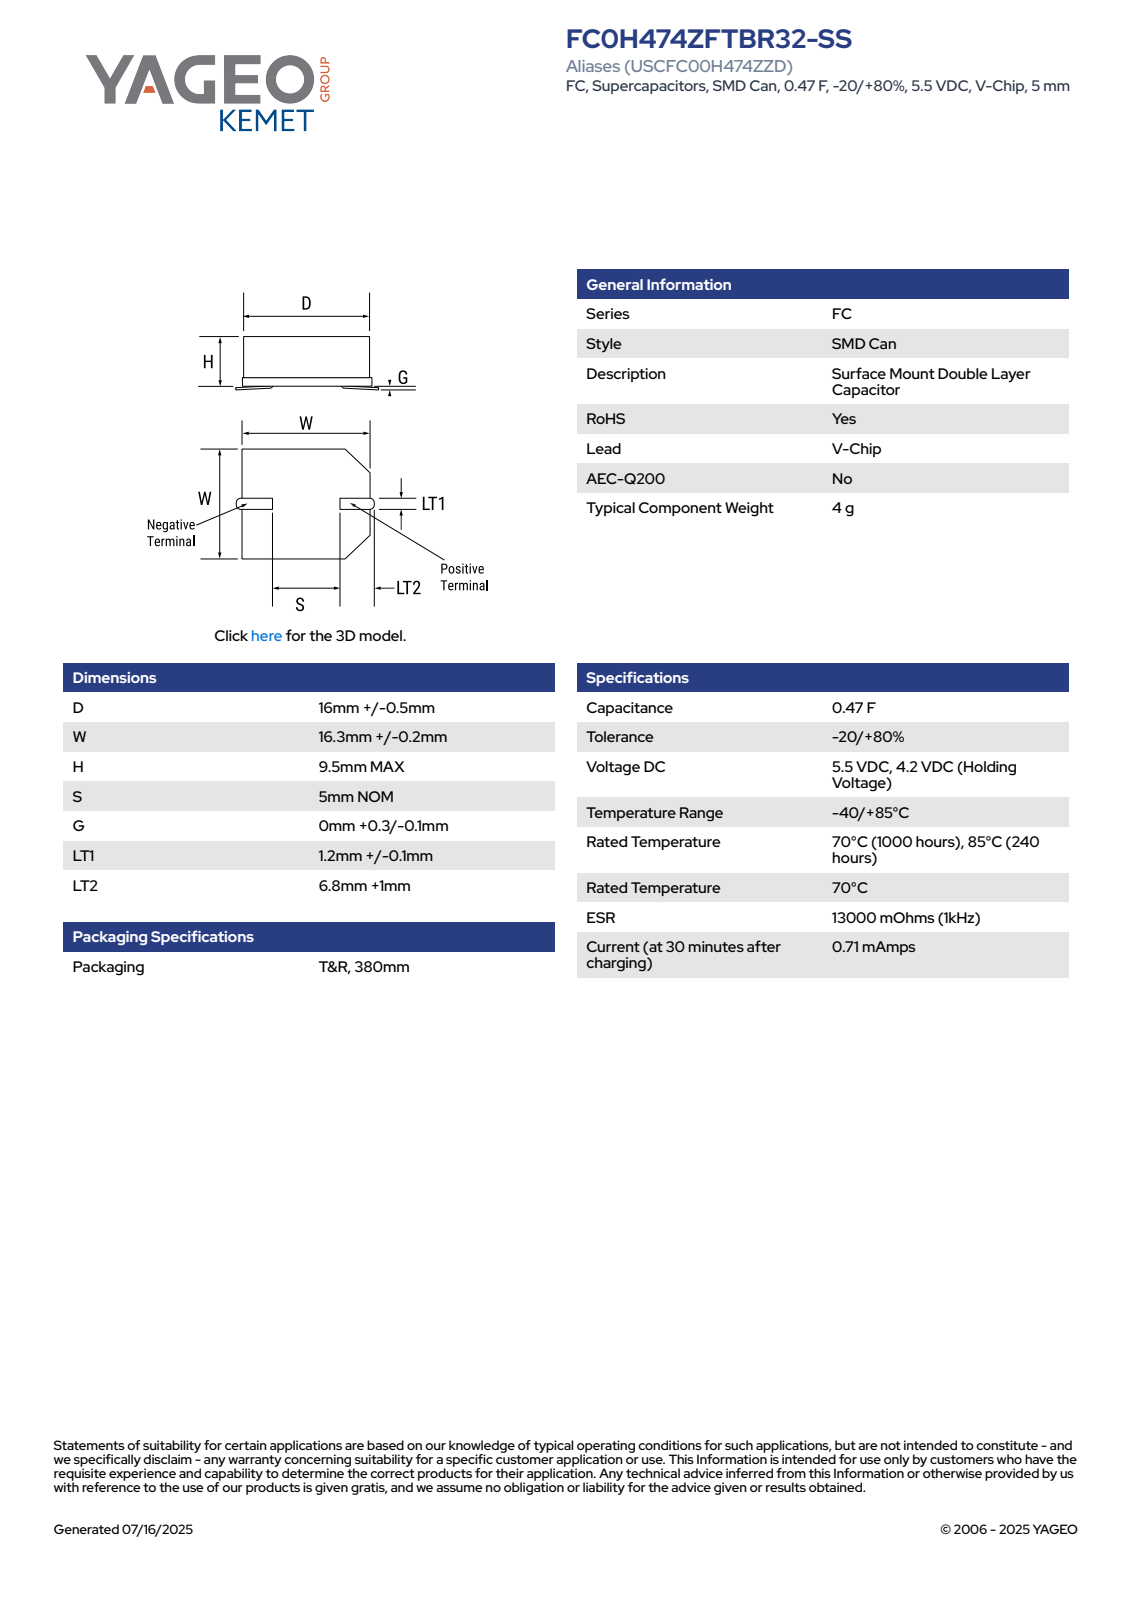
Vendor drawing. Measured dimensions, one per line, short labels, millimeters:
name: CDC_VC_D16L9.5LT11.3G0.3W16.5LT27.8
written by: SolidWorks 2014 (AUTOMOTIVE_DESIGN)
unit: mm
bodies: 5 solids, 60 faces (49 planar, 5 cylindrical, 6 other)
size: 20.6 × 16.5 × 9.51
volume: 1 979 mm³; area: 1 458 mm²
bosses: 1× ⌀16
rounds: 2× R0.2, 1× R6.35
face distances: 2.38, 9.2, 6.82, 9.21, 6.83, 16.5, 9.5, 2.68, 9.51, 7.6
